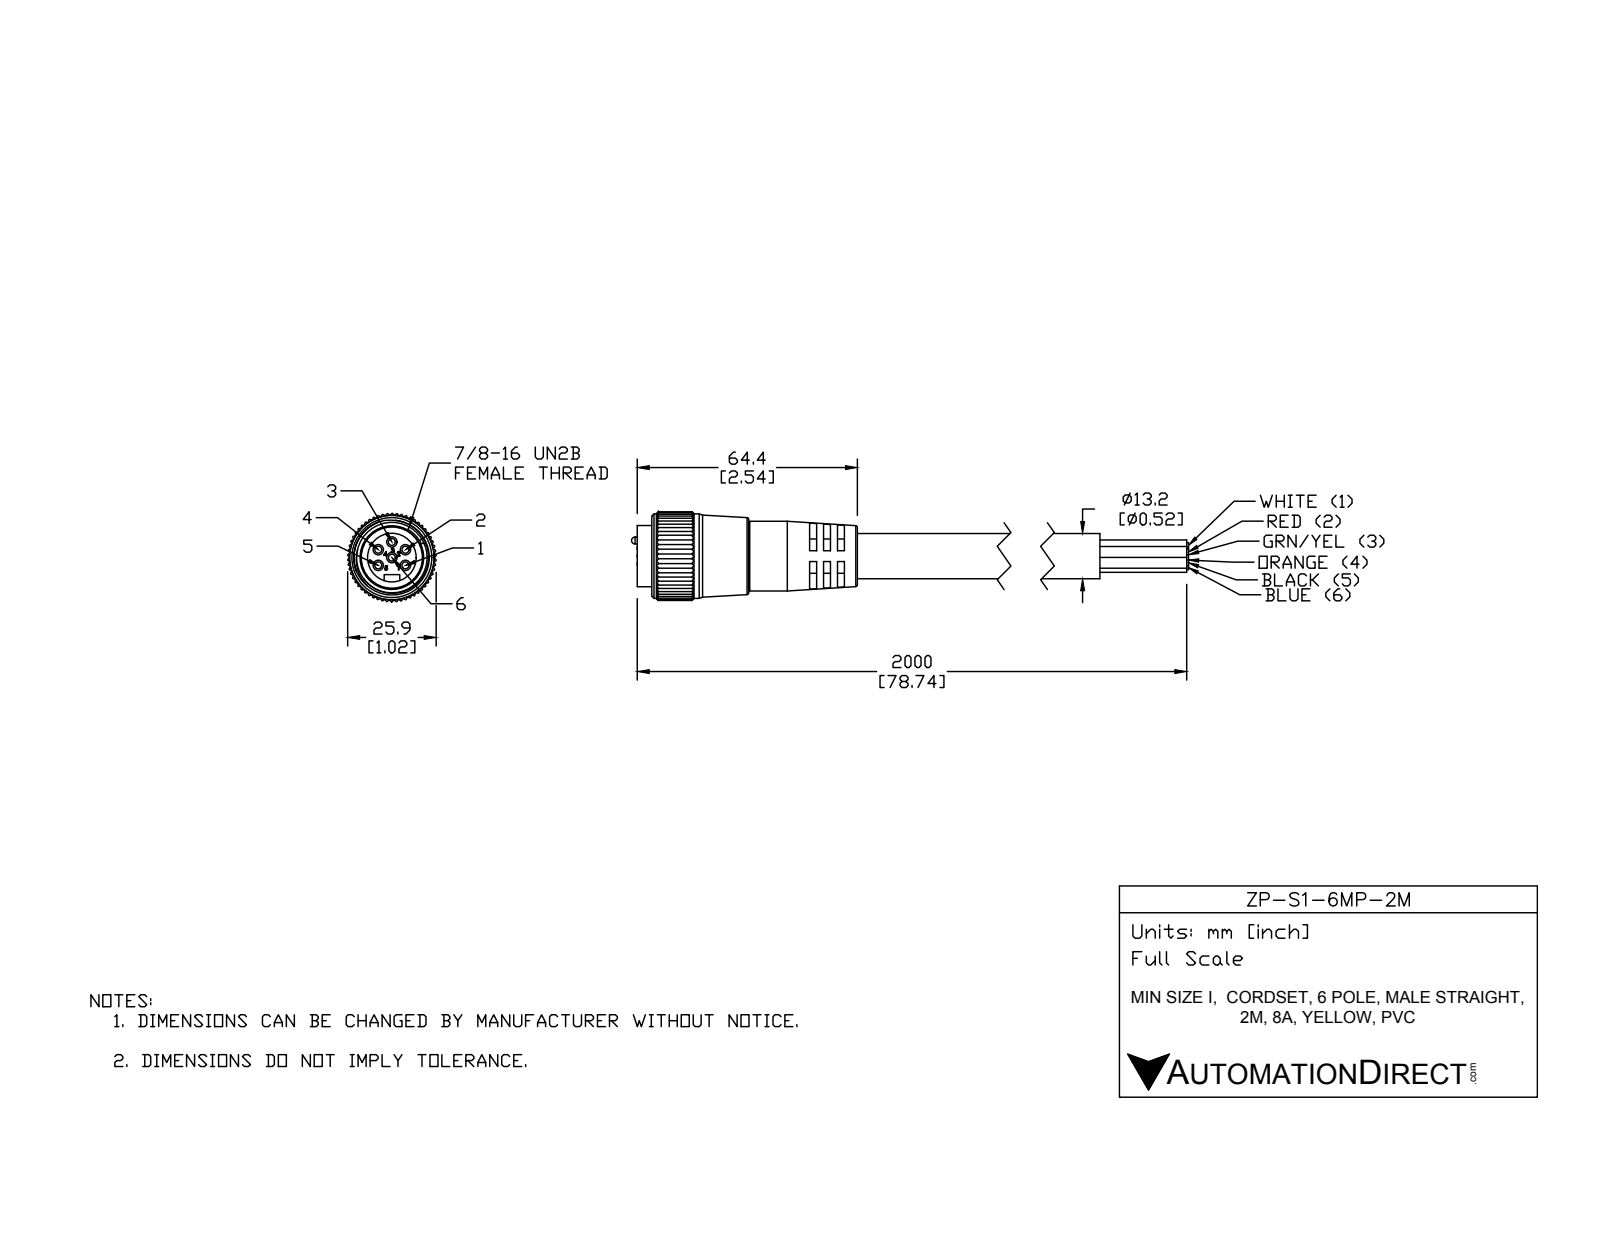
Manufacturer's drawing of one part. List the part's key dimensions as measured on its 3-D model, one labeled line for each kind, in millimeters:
Part name (STEP PRODUCT): ZP-S1-6MP-2M
STEP written by: SolidWorks 2015 (AUTOMOTIVE_DESIGN)
Units: millimetres
Bodies: 8 solids, 638 faces (229 planar, 326 cylindrical, 83 other)
Overall size (bounding box): 111.28 × 52.91 × 25.84
Volume: 31 376 mm³ · Surface area: 13 508 mm²
Round holes (diameter × count): ⌀14.22 ×1, ⌀19.96 ×1, ⌀20.45 ×1, ⌀21 ×1
Round bosses / shafts (diameter × count): ⌀3.05 ×6, ⌀2 ×6, ⌀13.21 ×2, ⌀24.68 ×1, ⌀20.4 ×1, ⌀19.5 ×1, ⌀17.88 ×1
Partial cylindrical surfaces — rounded edges, fillets, slot ends (radius × count): R0.25 ×165, R2.29 ×1, R5.25 ×1, R12.93 ×1
Main face-to-face distances: 2, 4.04, 2.04, 6.04, 2.02, 8.06, 6.06, 4.02, 4.03, 10.07
